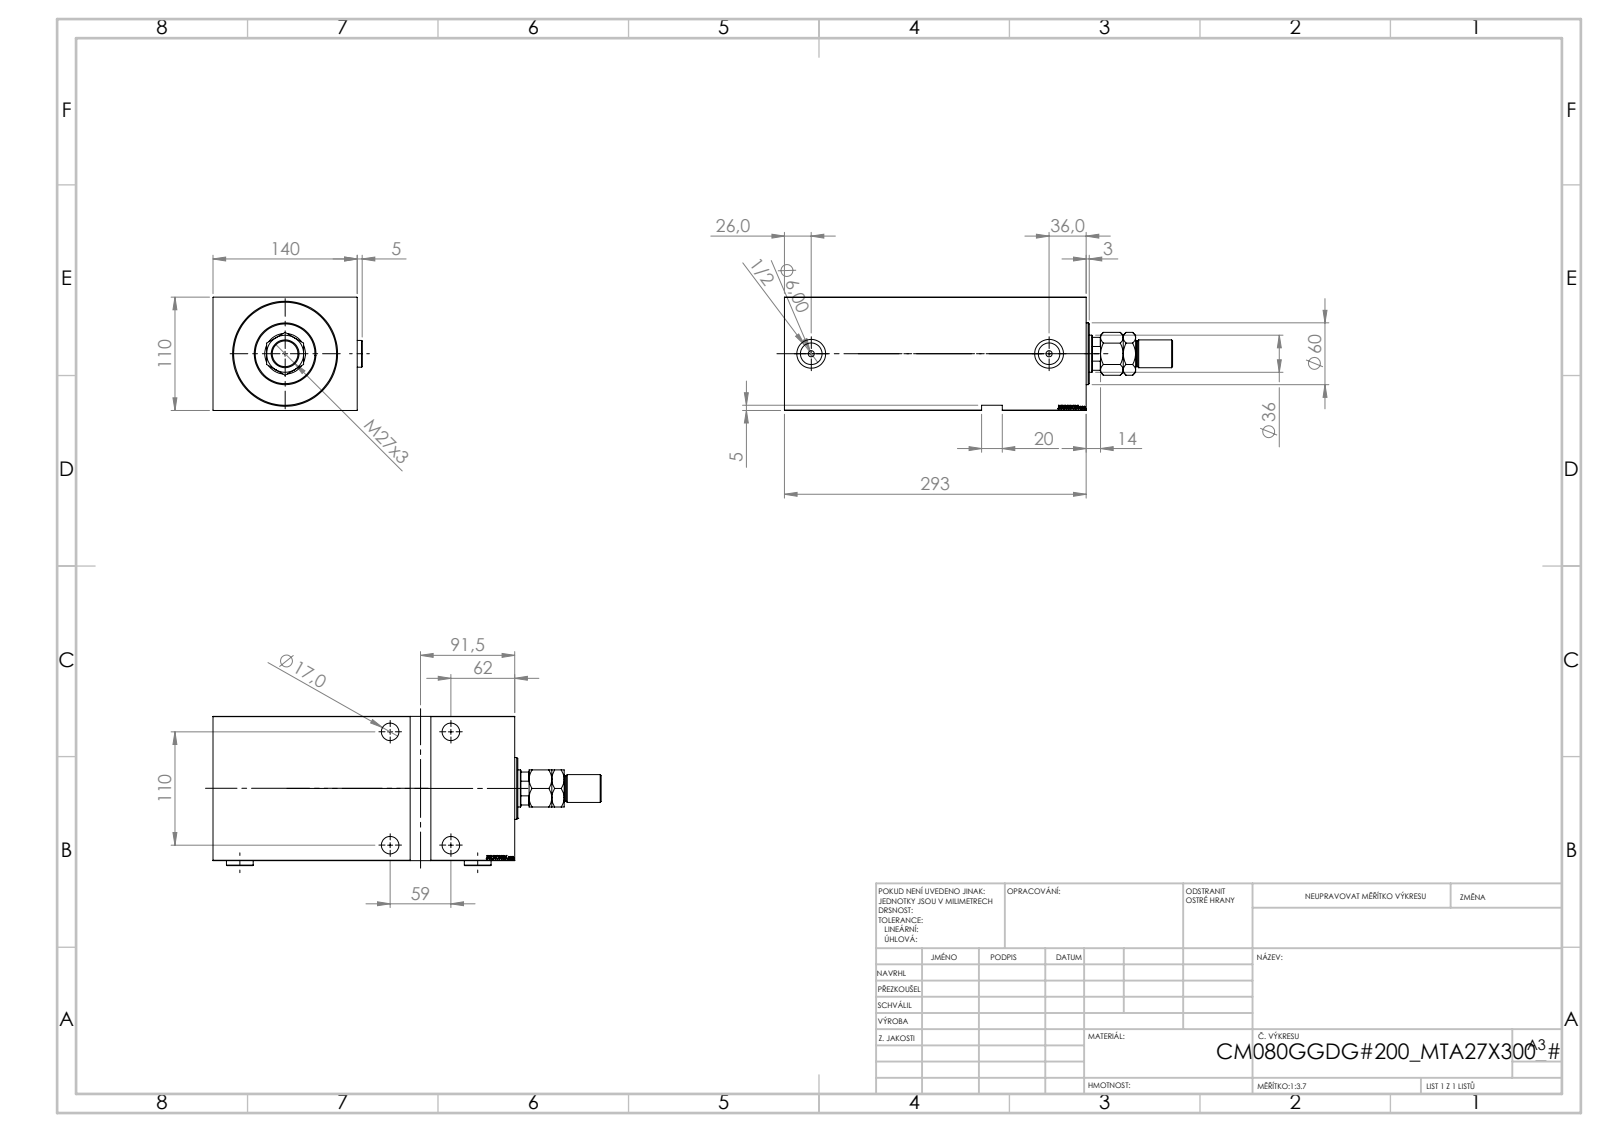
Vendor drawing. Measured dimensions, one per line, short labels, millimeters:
name: Zatka_OIL_PORT; V450CM_G_VCP; MTA; V450CM_VC_G (+1 more)
written by: SolidWorks 2019 (CONFIG_CONTROL_DESIGN)
unit: mm
bodies: 6 solids, 961 faces (461 planar, 72 cylindrical, 428 other)
size: 377 × 144.9 × 110
volume: 3 575 000 mm³; area: 357 667 mm²
holes: 4× ⌀17, 4× ⌀25, 2× ⌀6, 2× ⌀20.96, 2× ⌀28, 1× ⌀25.5, 1× ⌀36, 1× ⌀39.5, 1× ⌀80, 1× ⌀82, 1× ⌀100
bosses: 2× ⌀26, 1× ⌀60, 1× ⌀27, 1× ⌀25
rounds: 1× R17.5
face distances: 110, 140, 5, 293, 21, 272, 288, 267, 79, 58
hole spacings: 59, 110, 124.82, 231
